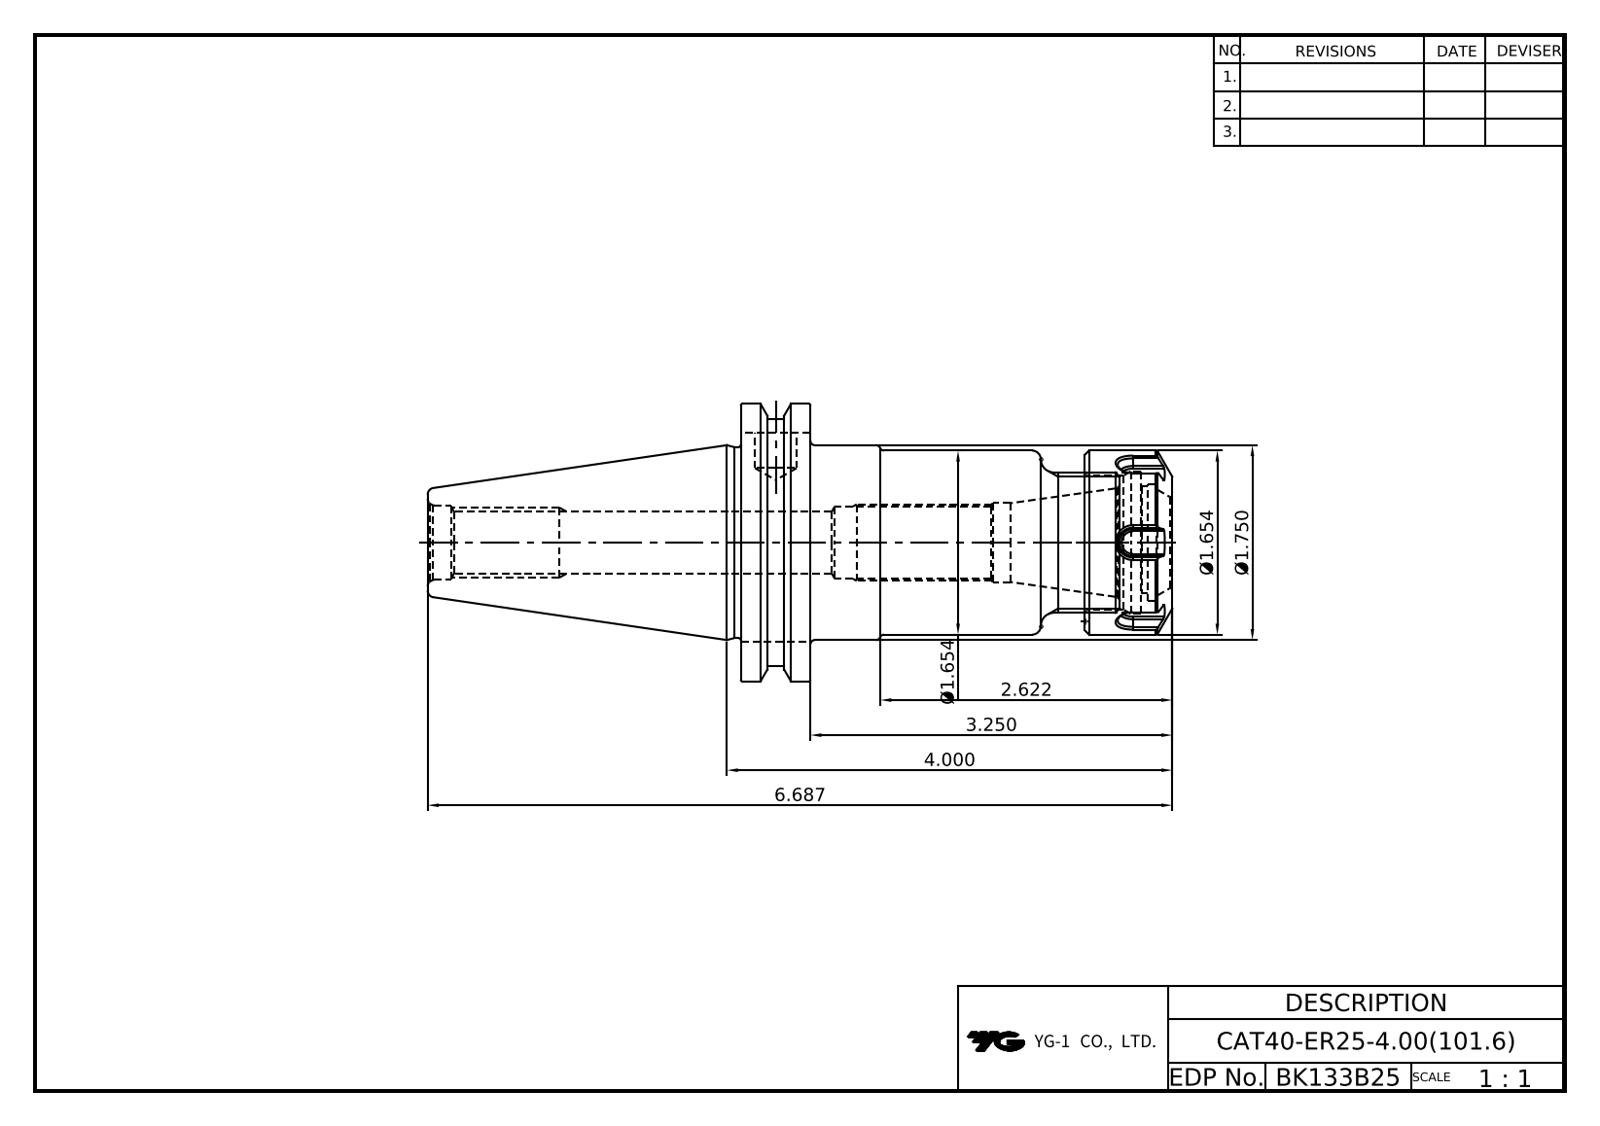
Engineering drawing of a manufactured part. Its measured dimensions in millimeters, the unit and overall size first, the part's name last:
Units: millimetres
Overall size (bounding box): 169.85 × 63.5 × 61.09
Round holes (diameter × count): ⌀9.53 ×1, ⌀13.39 ×1, ⌀15.75 ×1, ⌀16.3 ×1, ⌀18 ×1, ⌀20.9 ×1, ⌀23 ×1, ⌀26.8 ×1, ⌀30.5 ×1, ⌀32.5 ×1
Round bosses / shafts (diameter × count): ⌀63.5 ×1, ⌀56.3 ×1, ⌀44.45 ×1, ⌀43.6 ×1, ⌀42 ×1, ⌀32 ×1
Partial cylindrical surfaces — rounded edges, fillets, slot ends (radius × count): R0.5 ×12
Main face-to-face distances: 15.88, 68.43, 52.55, 78.43, 62.55, 10, 91.33, 75.45, 22.9, 12.9
Volume: 185 524 mm³ · Surface area: 39 300 mm²
Bodies: 2 solids, 143 faces (66 planar, 33 cylindrical, 44 other)
Part name (STEP PRODUCT): LO-CAT40-ER25-101.6; ER25NUT
STEP written by: Autodesk Inventor 2025 (AUTOMOTIVE_DESIGN)
